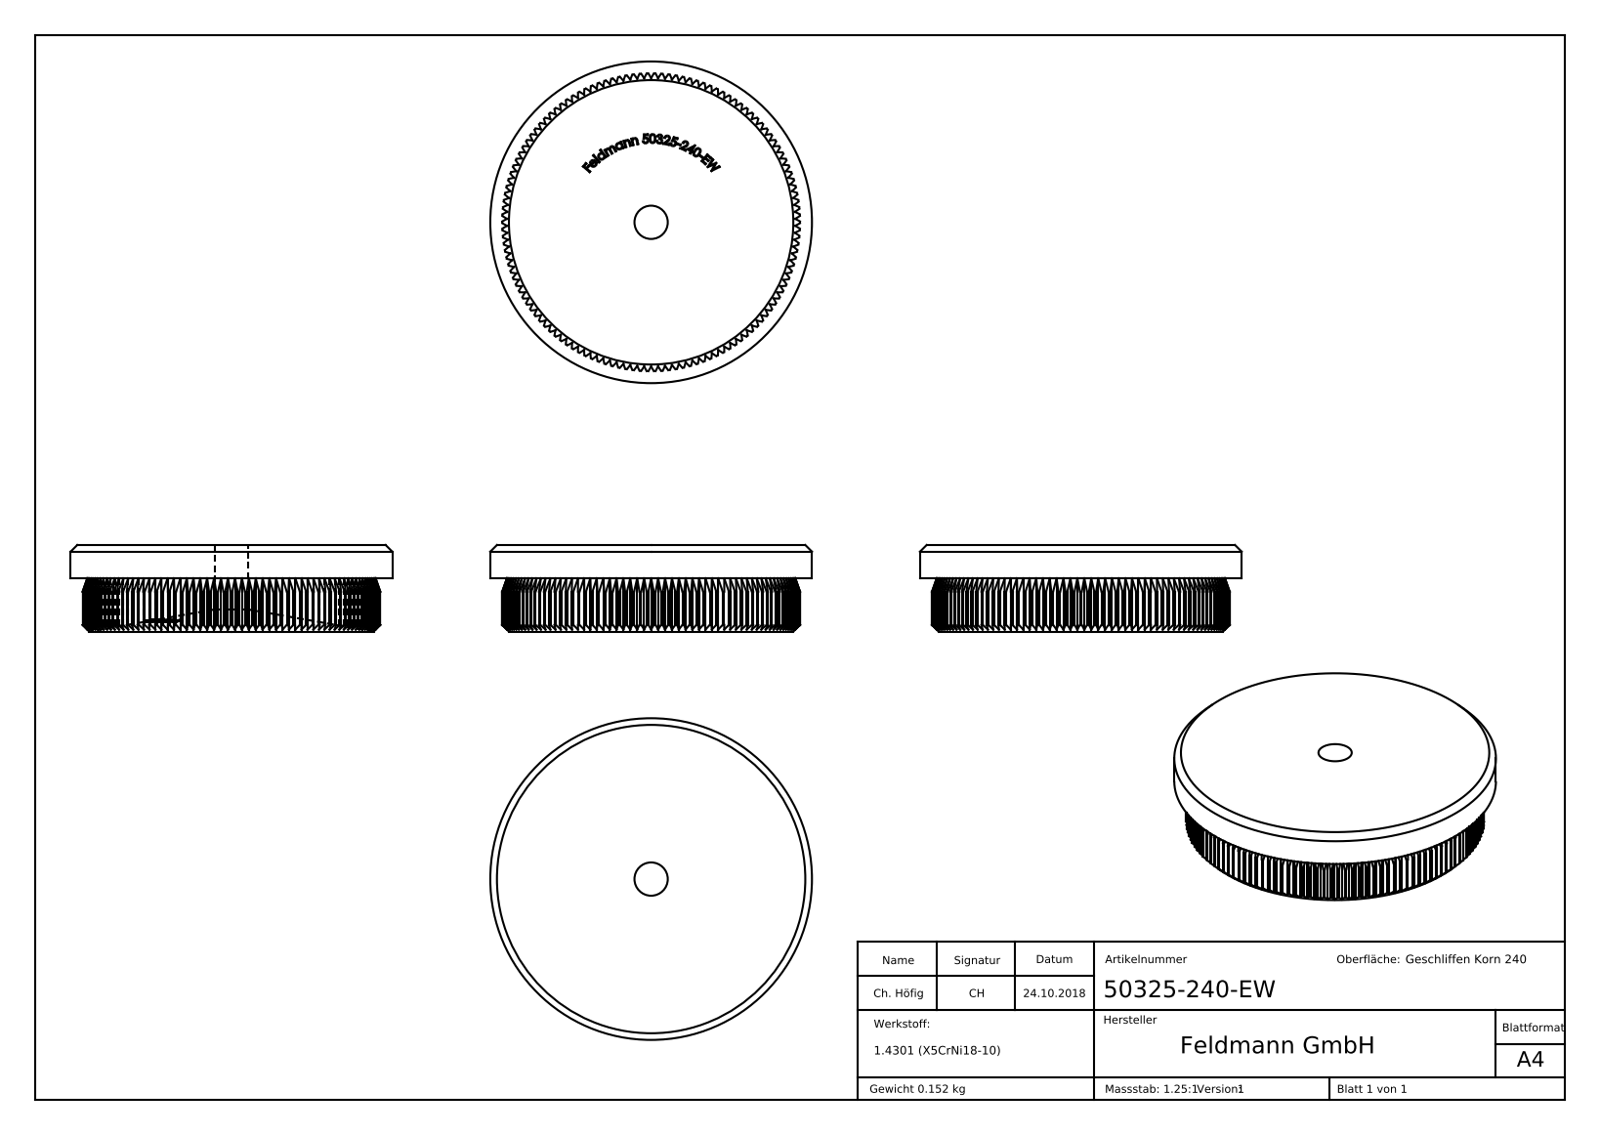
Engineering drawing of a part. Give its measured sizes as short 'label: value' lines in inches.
name: 50325-240-EW
written by: SolidWorks 2015 (CONFIG_CONTROL_DESIGN)
unit: in
bodies: 1 solid, 826 faces (405 planar, 134 cylindrical, 287 other)
size: 1.902 × 1.902 × 0.512
volume: 1.176 in³; area: 9.722 in²
holes: 1× ⌀0.197
bosses: 1× ⌀1.902
rounds: 1× R0.88
face distances: 0.197, 0.853, 0.852, 0.854, 0.851, 0.028, 0.021, 0.026, 0.052, 0.022
